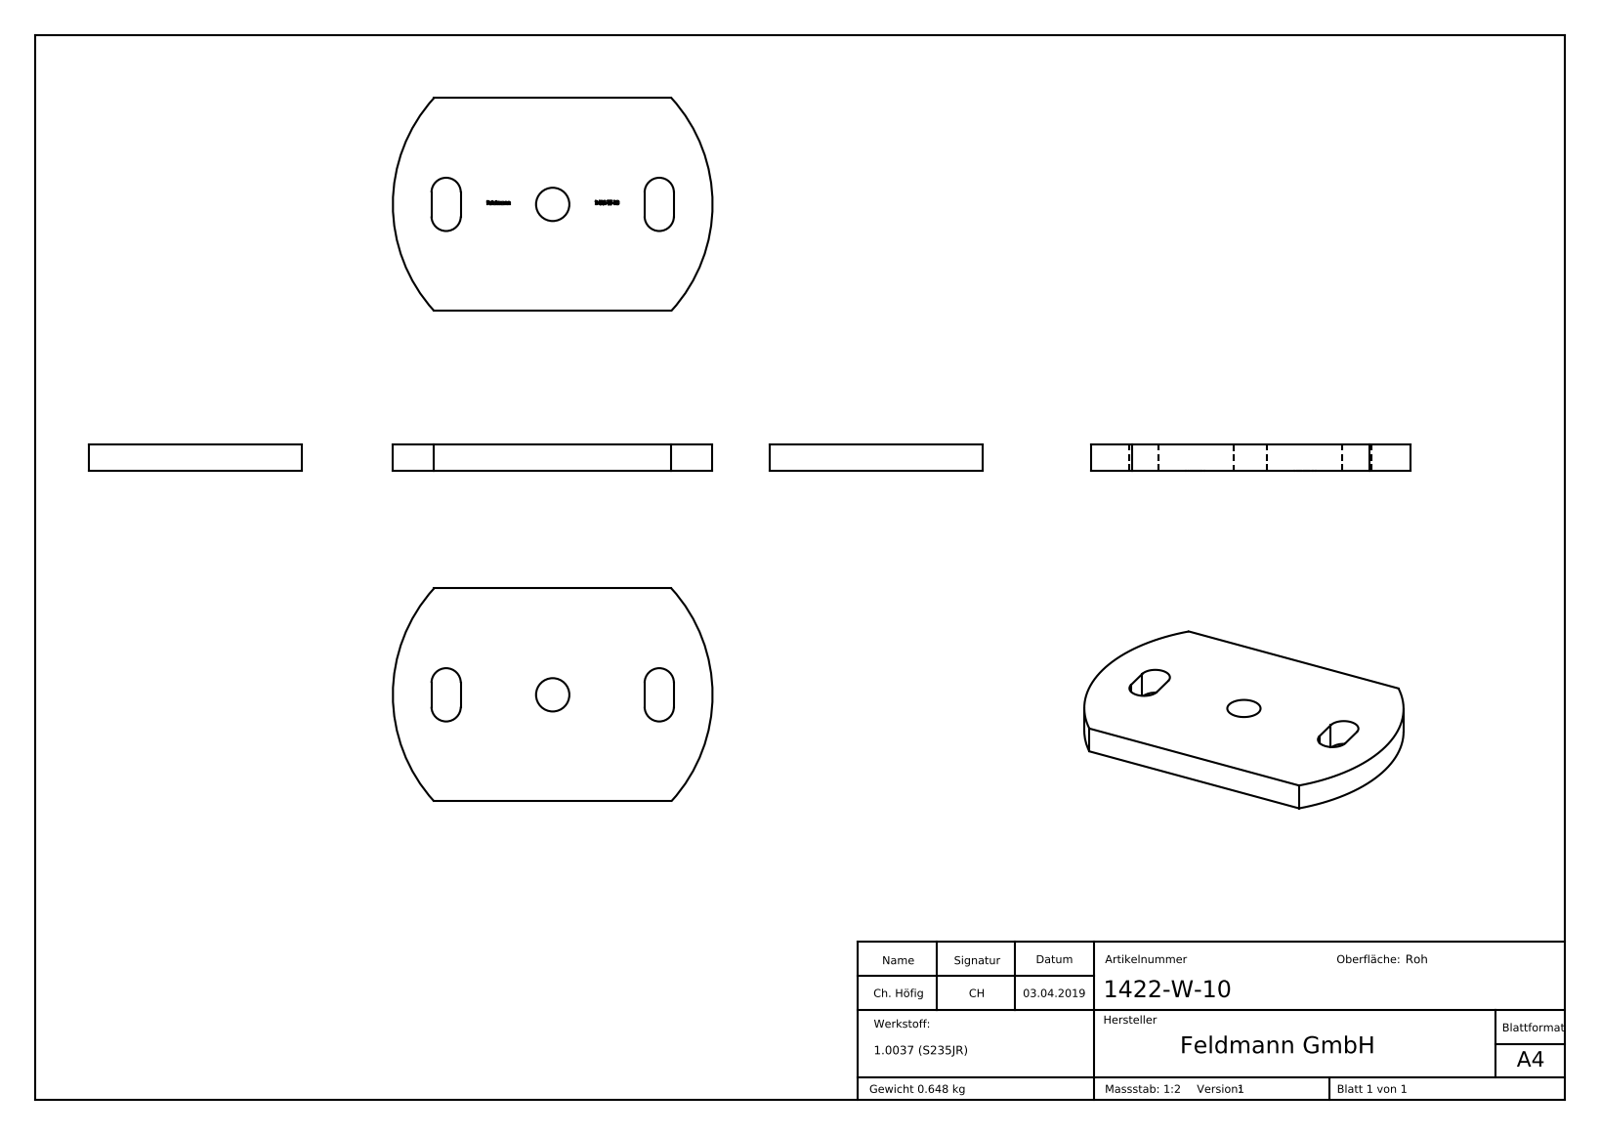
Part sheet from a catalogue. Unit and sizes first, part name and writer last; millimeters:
Units: millimetres
Overall size (bounding box): 120 × 80 × 10
Round holes (diameter × count): ⌀12.5 ×1
Partial cylindrical surfaces — rounded edges, fillets, slot ends (radius × count): R5.5 ×4, R59.36 ×2
Main face-to-face distances: 10, 80, 11, 91, 69, 9.9, 40, 0.44, 38.96, 45.95
Volume: 83 111 mm³ · Surface area: 21 611 mm²
Bodies: 1 solid, 221 faces (142 planar, 10 cylindrical, 69 other)
Part name (STEP PRODUCT): 1422-W-10
STEP written by: SolidWorks 2015 (CONFIG_CONTROL_DESIGN)
